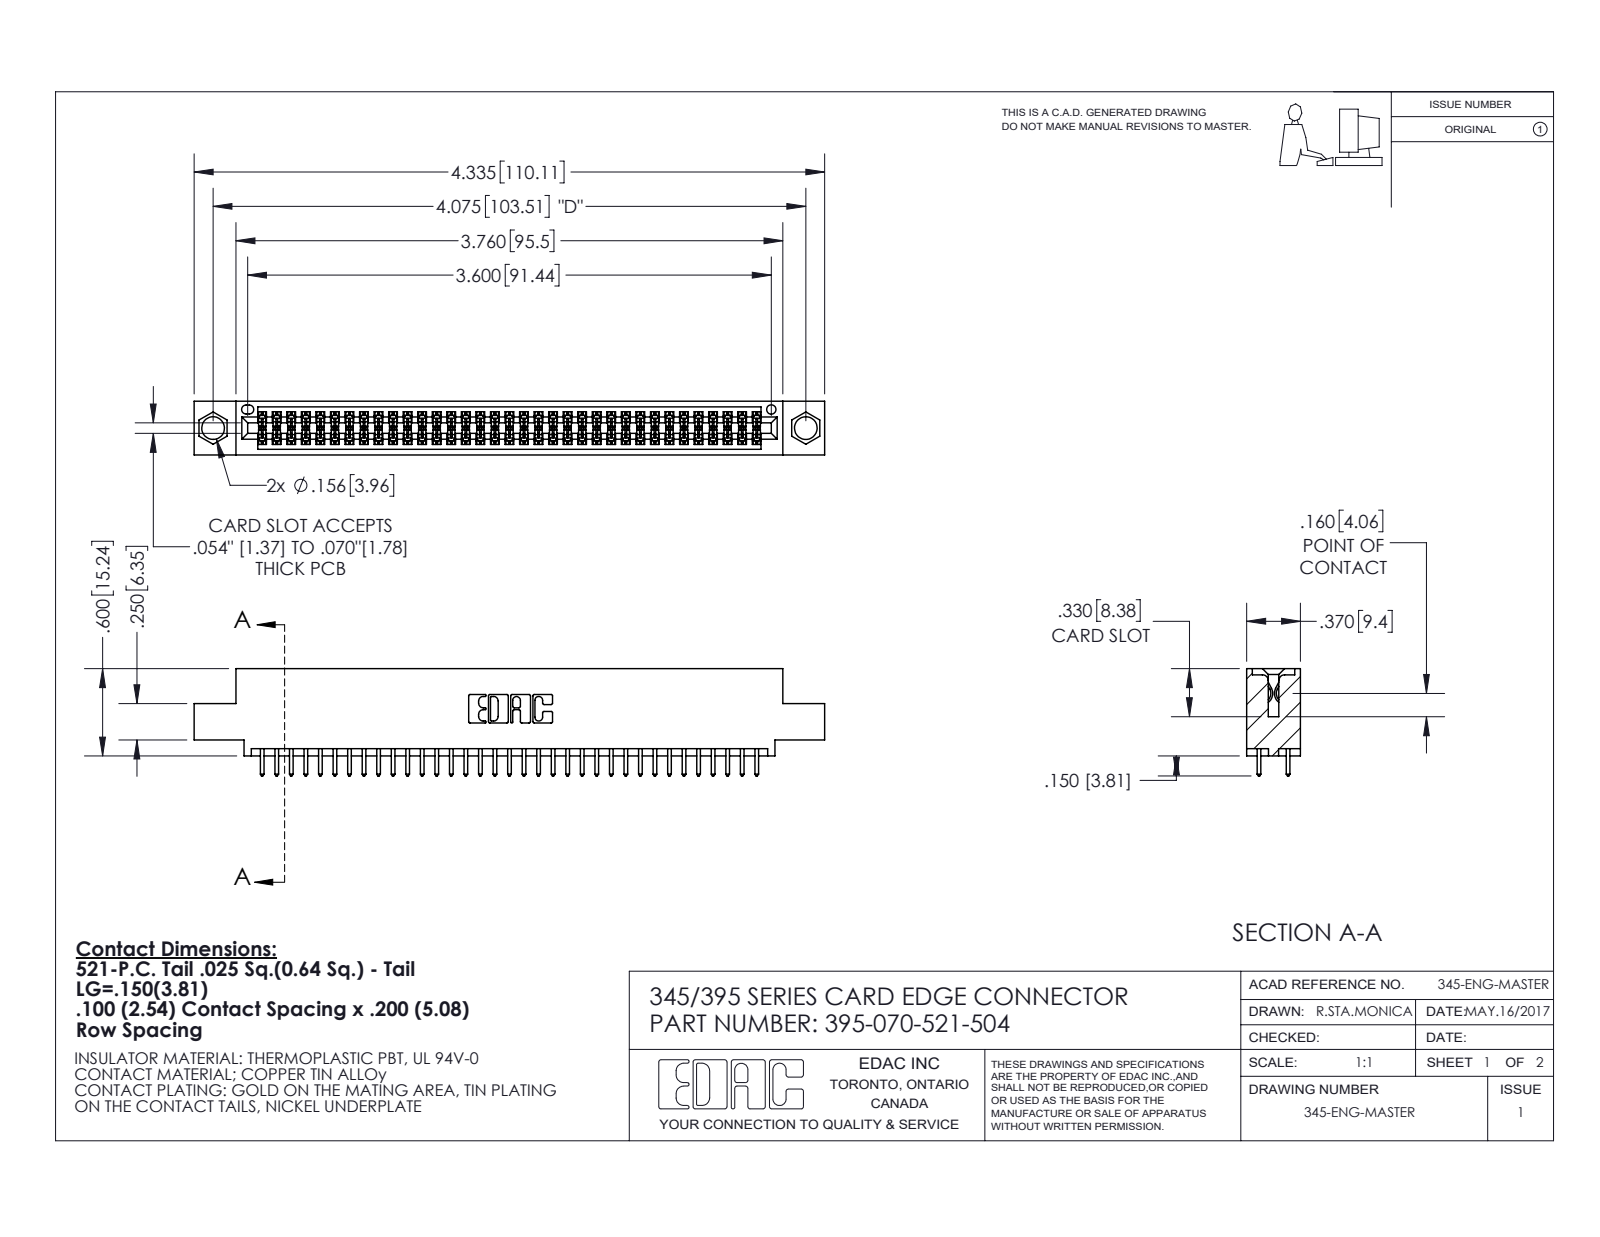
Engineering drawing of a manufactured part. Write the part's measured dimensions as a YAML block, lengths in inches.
part_name: "345 Part_0.110 Offset - 0.156 Dia-TI; 395-070-521-504; 345-292-001_345-293-121"
step_written_by: "SolidWorks 2020 (CONFIG_CONTROL_DESIGN)"
units: inches
bodies: {solids: 71, faces: 3644, planar: 2408, cylindrical: 1236, other: 0}
overall_size: [4.335, 0.737, 0.37]
volume: 0.636
surface_area: 23.3
round_holes:
  - {diameter: 0.156, count: 2}
  - {diameter: 0.064, count: 1}
partial_cylinders:
  - {radius: 0.006, count: 140}
  - {radius: 0.01, count: 70}
  - {radius: 0.01, count: 22}
  - {radius: 0.007, count: 6}
  - {radius: 0.031, count: 6}
  - {radius: 0.026, count: 3}
  - {radius: 0.014, count: 2}
  - {radius: 0.019, count: 2}
face_to_face_distances: [0.072, 0.298, 0.2, 0.37, 0.098, 0.272, 0.025, 0.225, 0.175, 0.149]
hole_center_spacings: [0.27, 3.839, 4.075]
